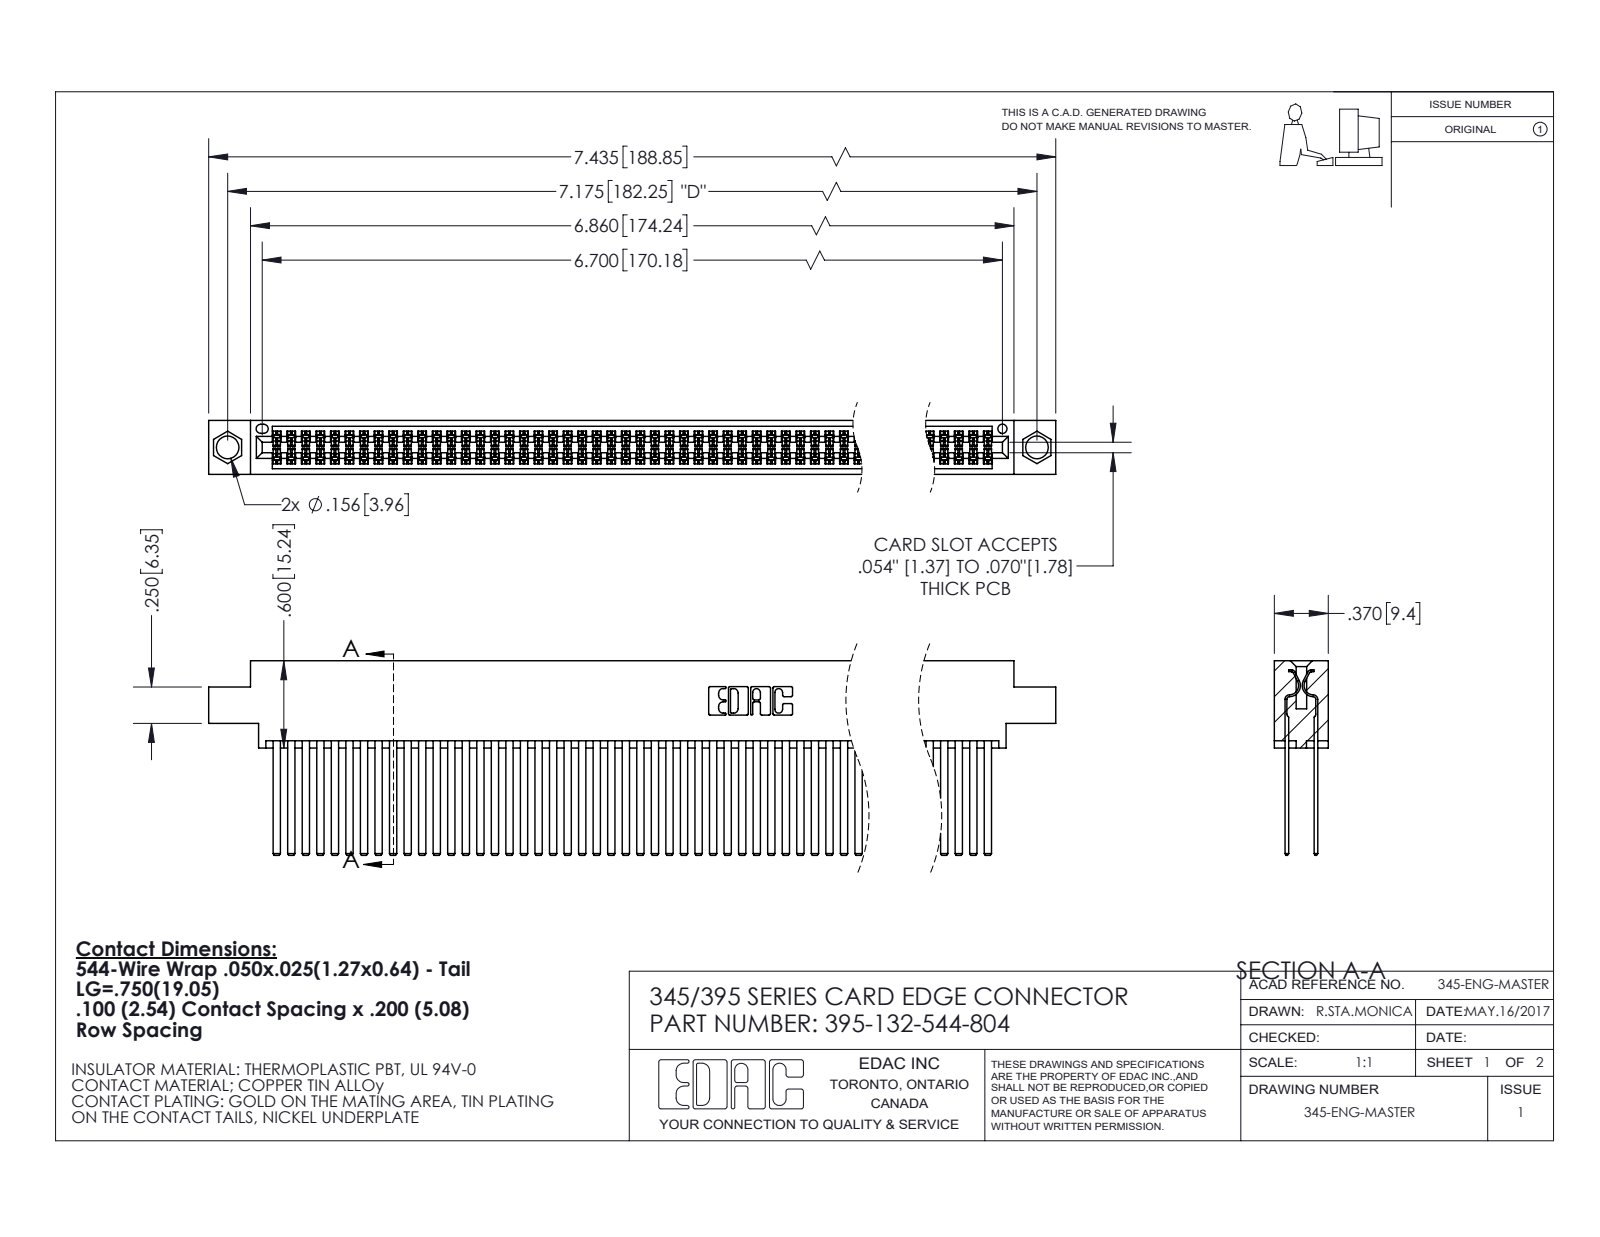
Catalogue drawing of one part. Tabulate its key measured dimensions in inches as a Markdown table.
| quantity | value |
| --- | --- |
| part name | 345 Part_0.170 Offset - 0.156 Dia-TI; 395-132-544-804; 345-292-001_345-293-144 |
| STEP written by | SolidWorks 2020 (CONFIG_CONTROL_DESIGN) |
| units | inches |
| bodies | 133 solids, 5952 faces (3926 planar, 2026 cylindrical, 0 other) |
| overall size | 7.435 × 1.337 × 0.37 |
| volume | 1.233 in³ |
| surface area | 55.4 in² |
| round holes (diameter × count) | 0.156 × 2, 0.064 × 1 |
| partial cylindrical surfaces (radius × count) | 0.006 × 198, 0.01 × 22, 0.007 × 6, 0.031 × 6, 0.026 × 3, 0.014 × 2, 0.019 × 2, 0.022 × 2 |
| main face-to-face distances | 0.2, 0.025, 0.072, 0.098, 0.272, 0.298, 0.225, 0.175, 0.37, 0.15 |
| hole center spacings | 0.27, 6.939, 7.175 |
